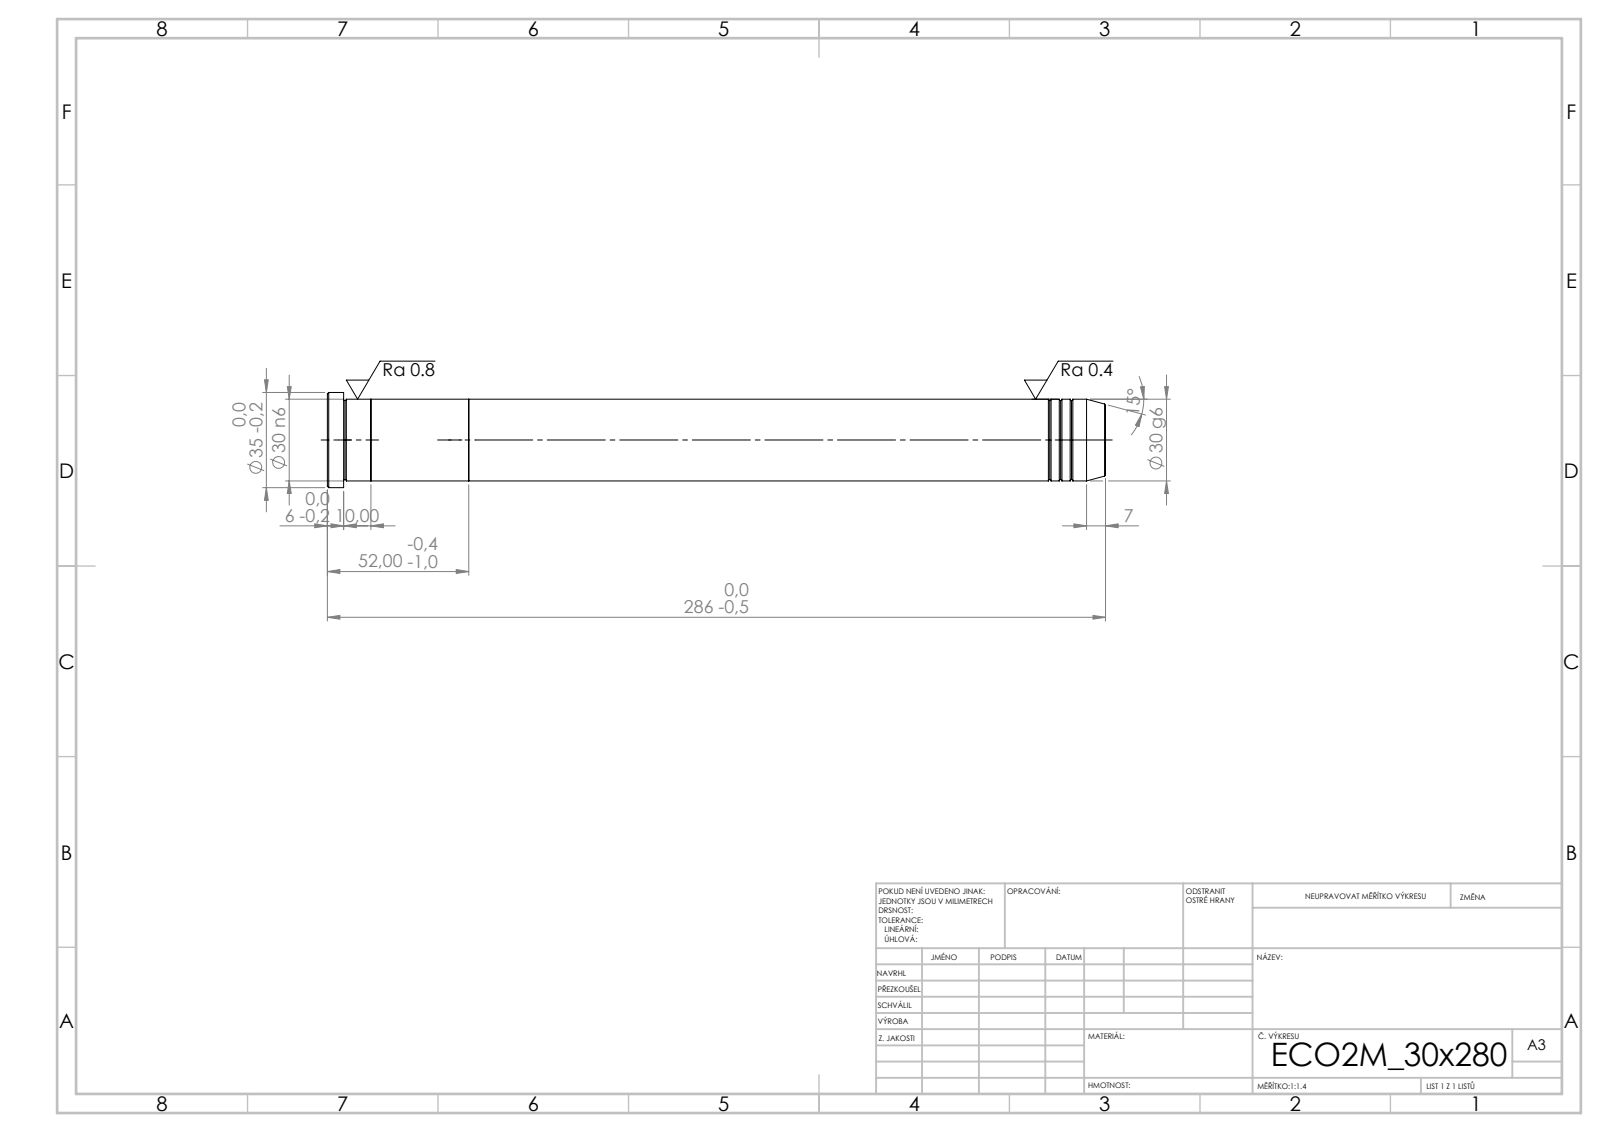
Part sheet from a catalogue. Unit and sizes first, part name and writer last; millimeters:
Units: millimetres
Overall size (bounding box): 286 × 35 × 35
Round bosses / shafts (diameter × count): ⌀35 ×1, ⌀30 ×1
Main face-to-face distances: 36, 52, 16, 234, 270, 286, 280, 46, 10, 6
Volume: 202 938 mm³ · Surface area: 31 776 mm²
Bodies: 3 solids, 43 faces (7 planar, 14 cylindrical, 22 other)
STEP written by: SolidWorks 2019 (CONFIG_CONTROL_DESIGN)
